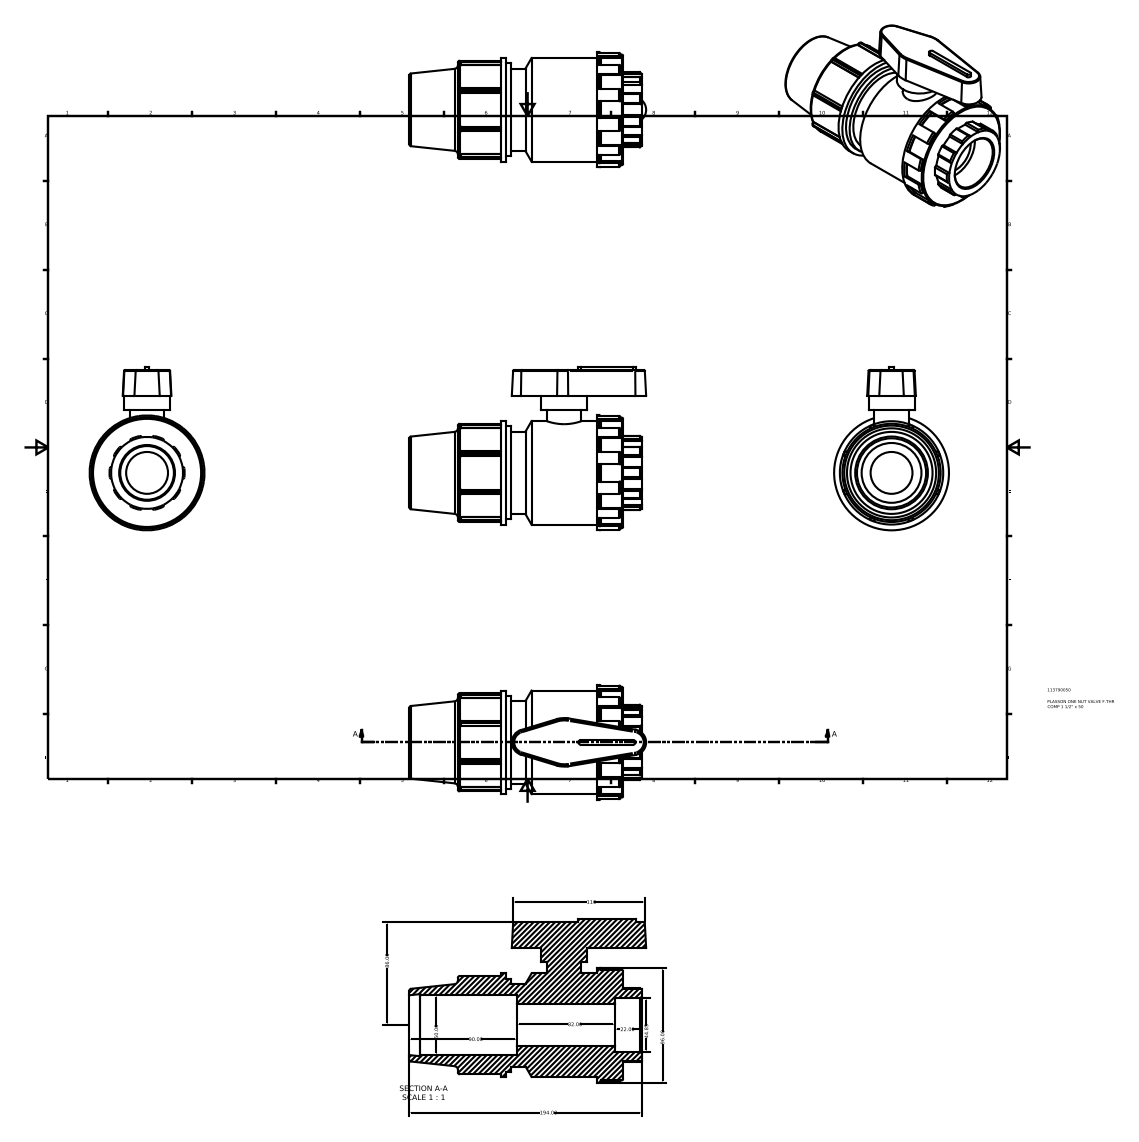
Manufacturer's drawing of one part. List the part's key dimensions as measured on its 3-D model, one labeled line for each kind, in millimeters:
Part name (STEP PRODUCT): 113790050
STEP written by: Autodesk Inventor 2015 (AUTOMOTIVE_DESIGN)
Units: millimetres
Bodies: 1 solid, 248 faces (99 planar, 74 cylindrical, 75 other)
Overall size (bounding box): 197.86 × 136.58 × 96
Volume: 755 501 mm³ · Surface area: 103 311 mm²
Round holes (diameter × count): ⌀35 ×1, ⌀44.84 ×1, ⌀50 ×1
Round bosses / shafts (diameter × count): ⌀96 ×1, ⌀92.16 ×1, ⌀86.4 ×1, ⌀82.08 ×1, ⌀77.76 ×1, ⌀69.12 ×1, ⌀38.4 ×1, ⌀28.8 ×1
Partial cylindrical surfaces — rounded edges, fillets, slot ends (radius × count): R1.34 ×20, R1.5 ×16, R0.9 ×4, R1.92 ×2, R30.05 ×1, R31.39 ×1
Main face-to-face distances: 21.5, 22, 15.4, 37.4, 75.6, 97.6, 113, 40.5, 4.68, 9
